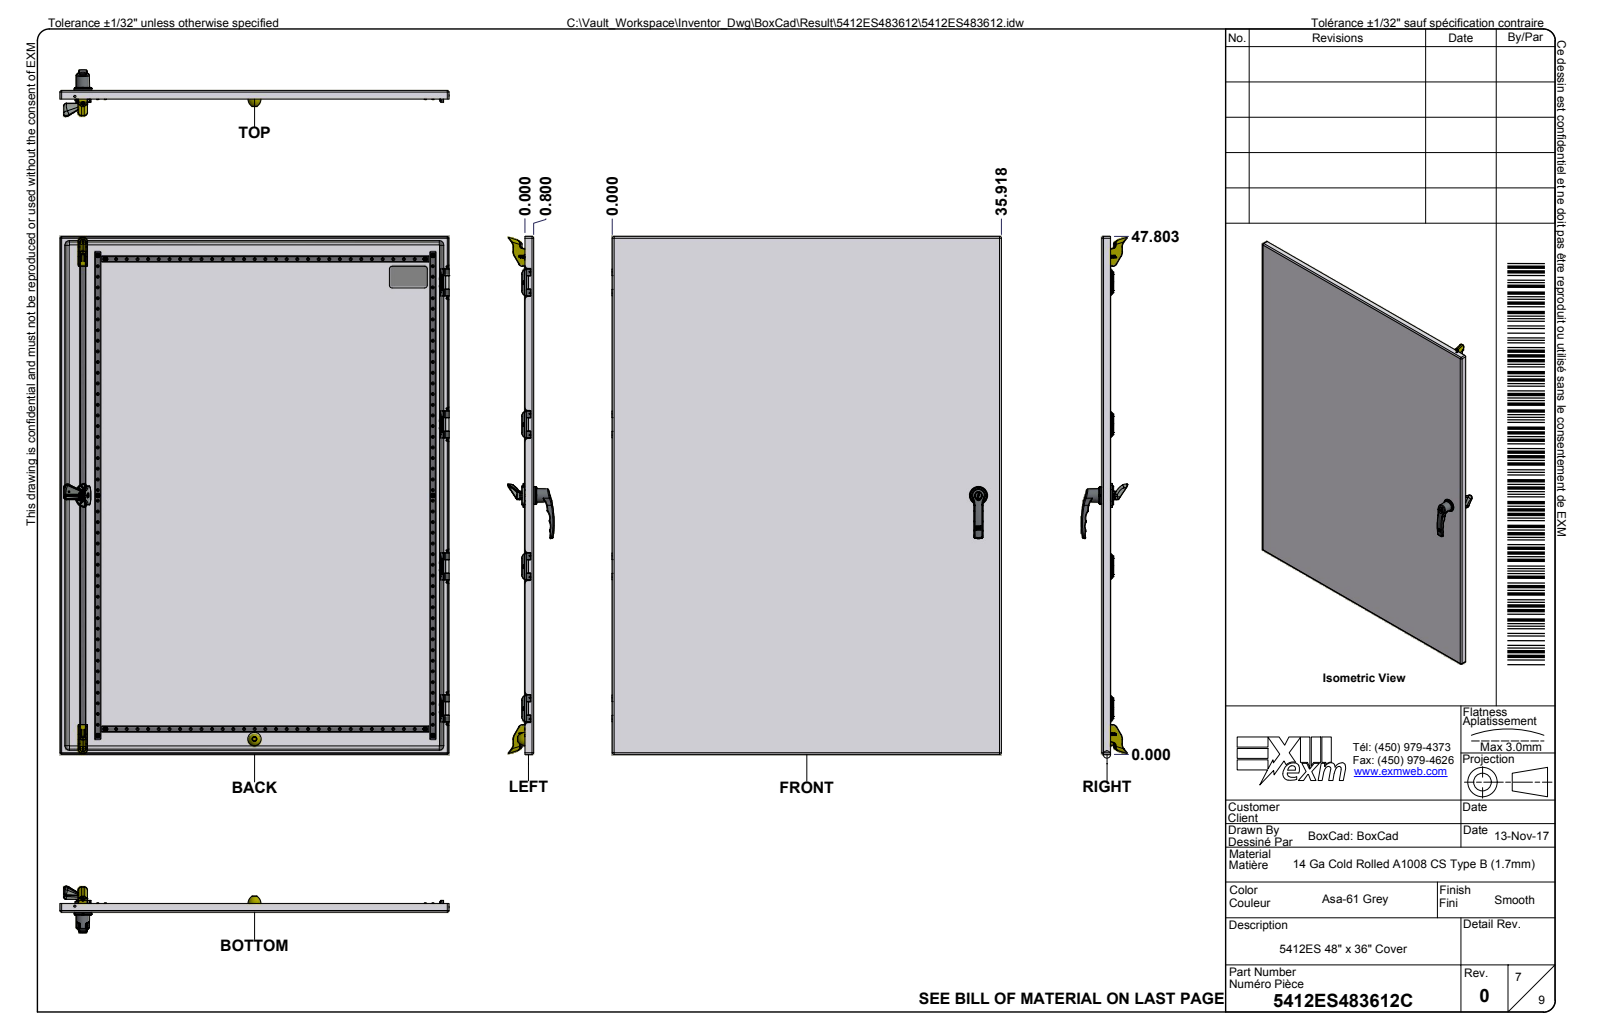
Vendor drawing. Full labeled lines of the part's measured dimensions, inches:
Part name (STEP PRODUCT): 5412ES483612; 5412ES483612B; 5412ES483612B-P; STK-Q-16005 (+8 more)
STEP written by: Autodesk Inventor 2024 (AUTOMOTIVE_DESIGN)
Units: inches
Bodies: 123 solids, 21688 faces (6208 planar, 5329 cylindrical, 10151 other)
Overall size (bounding box): 48 × 36.018 × 14.985
Volume: 605.3 in³ · Surface area: 15 912 in²
Round holes (diameter × count): ⌀0.165 ×88, ⌀0.03 ×18, ⌀0.043 ×16, ⌀0.315 ×14, ⌀0.201 ×13, ⌀0.311 ×11, ⌀0.178 ×8, ⌀0.27 ×8, ⌀0.197 ×6, ⌀0.268 ×6, ⌀0.5 ×5, ⌀0.187 ×4
Round bosses / shafts (diameter × count): ⌀0.237 ×88, ⌀0.03 ×18, ⌀0.039 ×16, ⌀0.232 ×15, ⌀0.717 ×8, ⌀0.311 ×8, ⌀0.262 ×8, ⌀0.177 ×7
Partial cylindrical surfaces — rounded edges, fillets, slot ends (radius × count): R0.02 ×458, R0.01 ×340, R0.039 ×308, R0.008 ×168, R0.016 ×58, R0.079 ×56, R0.012 ×48, R0.059 ×46
Main face-to-face distances: 0.068, 13.052, 12.983, 13.12, 0.942, 0.874, 12.109, 12.178, 1.047, 0.979
Hole centre spacings: 13.101, 26.202, 0.35, 0.735, 1.052, 1.385, 1.969, 13.101
